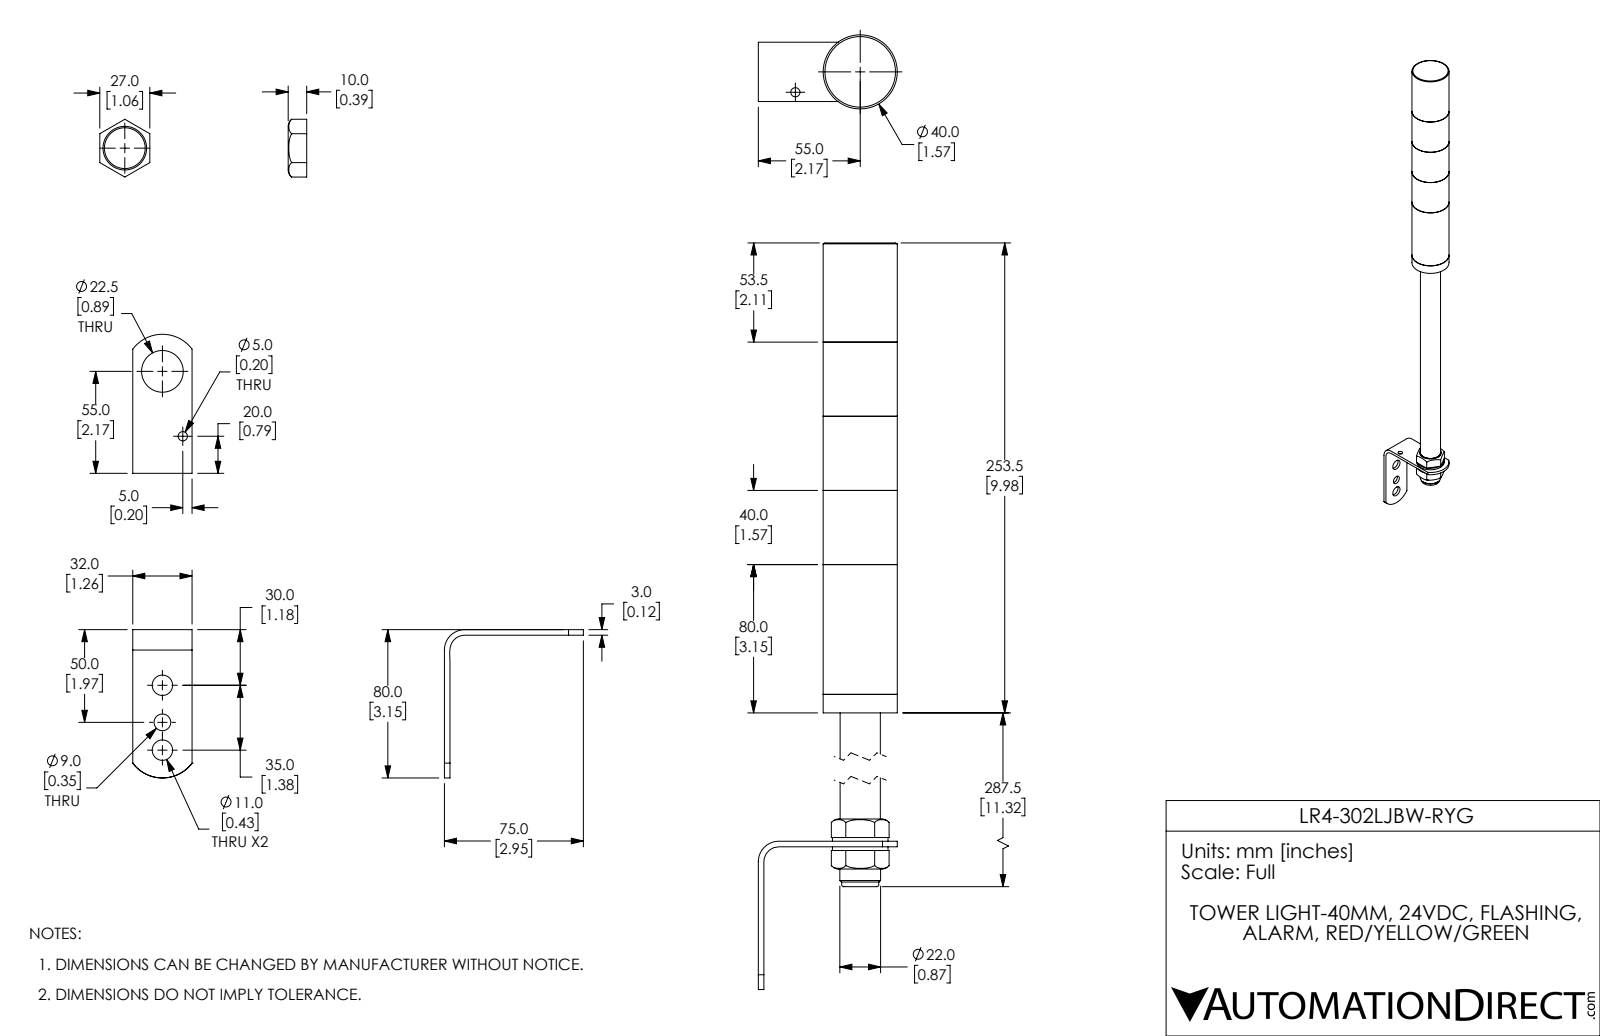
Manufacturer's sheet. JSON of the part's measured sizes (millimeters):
{"part_name": "LR4-302LJBW-RYG", "step_written_by": "SolidWorks 2017 (AUTOMOTIVE_DESIGN)", "units": "millimeters", "bodies": {"solids": 12, "faces": 159, "planar": 58, "cylindrical": 87, "other": 14}, "overall_size": [596.5, 75, 40], "volume_mm3": 383300, "surface_area_mm2": 116800, "round_holes": [[3.2, 2], [11, 2], [5, 1], [7.7, 1], [9, 1], [17.7, 1], [22, 1], [22.5, 1], [27.6, 1], [35.2, 1], [35.3, 1], [37.2, 1]], "round_bosses_or_shafts": [[40, 1], [37.1, 1], [34.7, 1], [30, 1], [21.7, 1]], "partial_cylinders_radius": [[20, 1]], "face_to_face_distances": [40, 80, 80.3, 120.3, 120, 90.3, 83.2, 10.3, 66, 106], "hole_center_spacings": [7.2, 14.4, 15, 20, 29.9, 35, 36.7, 43.6]}
